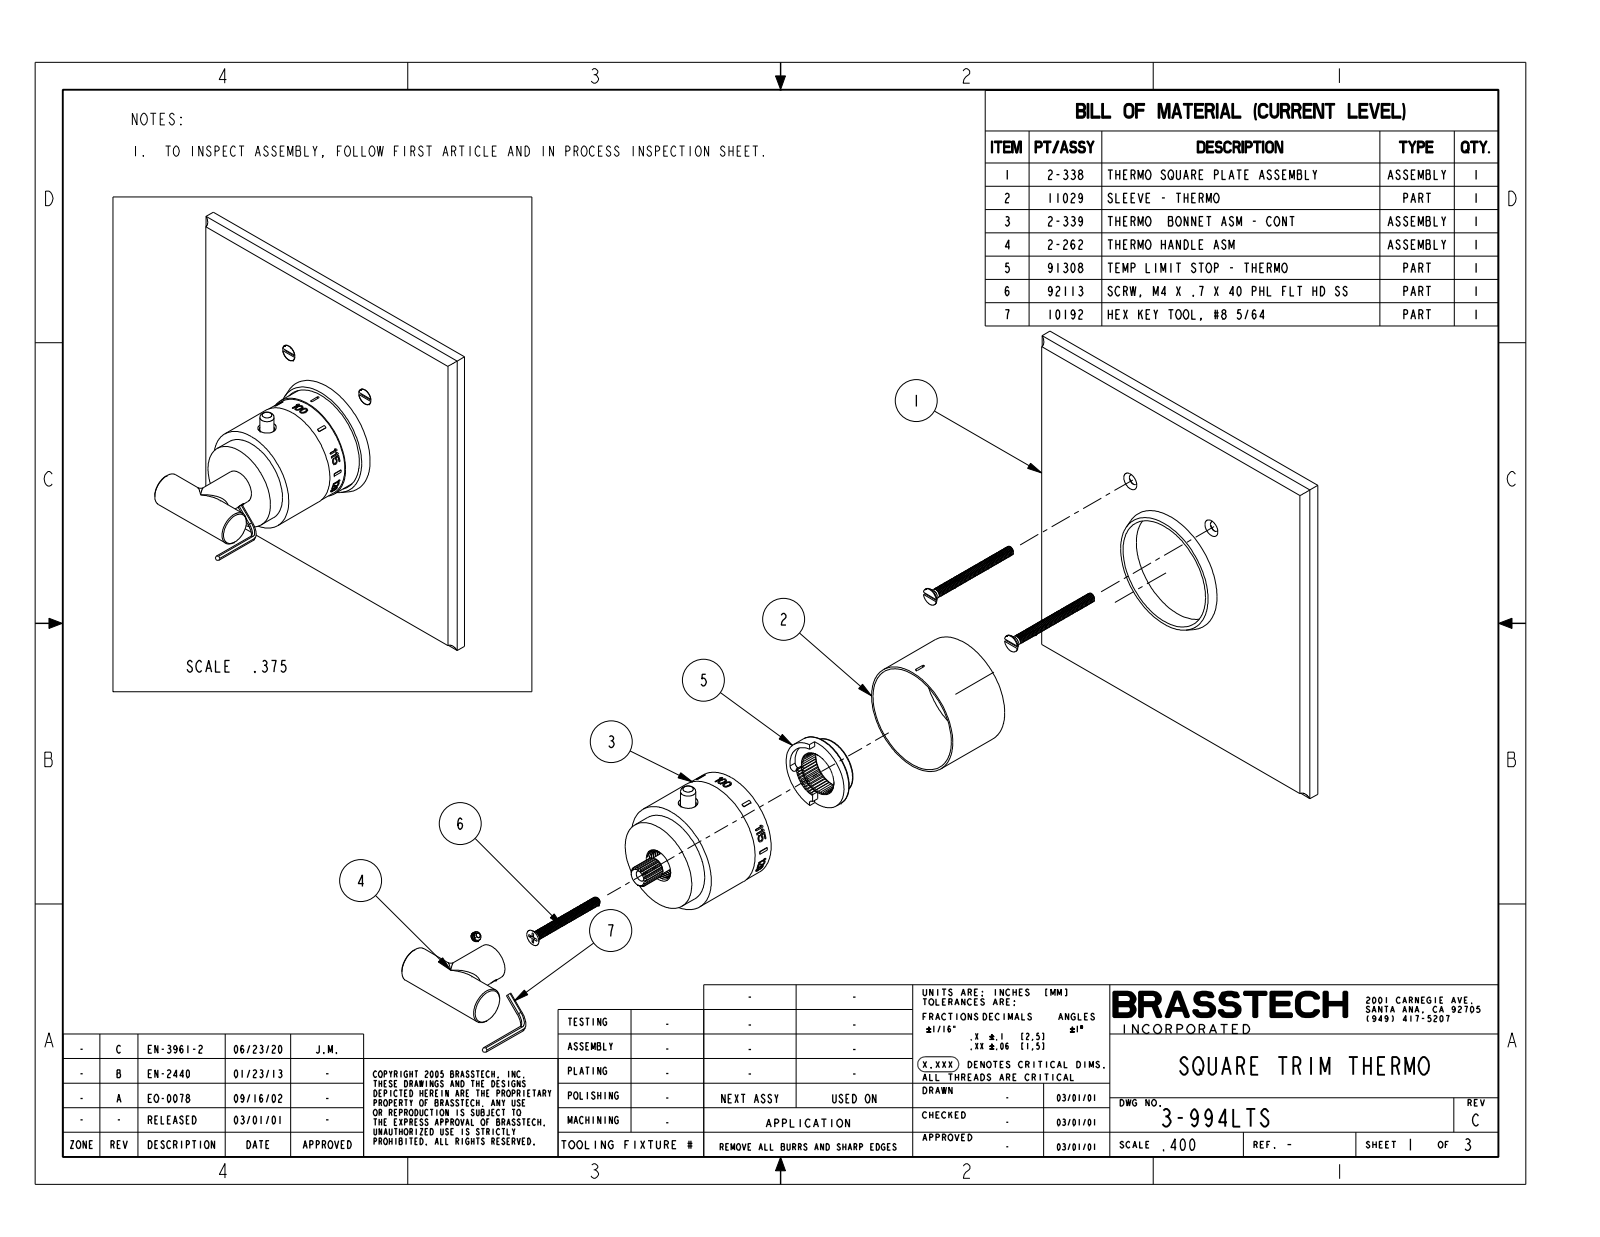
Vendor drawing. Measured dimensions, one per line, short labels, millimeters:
name: 3-994LTS
written by: CREO PARAMETRIC BY PTC INC, 2018400 (CONFIG_CONTROL_DESIGN)
unit: mm
bodies: 1 solid, 385 faces (333 planar, 40 cylindrical, 12 other)
size: 165.1 × 165.1 × 99
volume: 330 900 mm³; area: 70 970 mm²
bosses: 2× ⌀16, 1× ⌀50, 1× ⌀49.3, 1× ⌀49, 1× ⌀41, 1× ⌀6.6, 1× ⌀1.7
rounds: 4× R3.2, 1× R24.6
face distances: 8, 165.1, 65.6, 57.6, 57.6, 49.7, 7.9, 59.9, 105.2, 45.2
